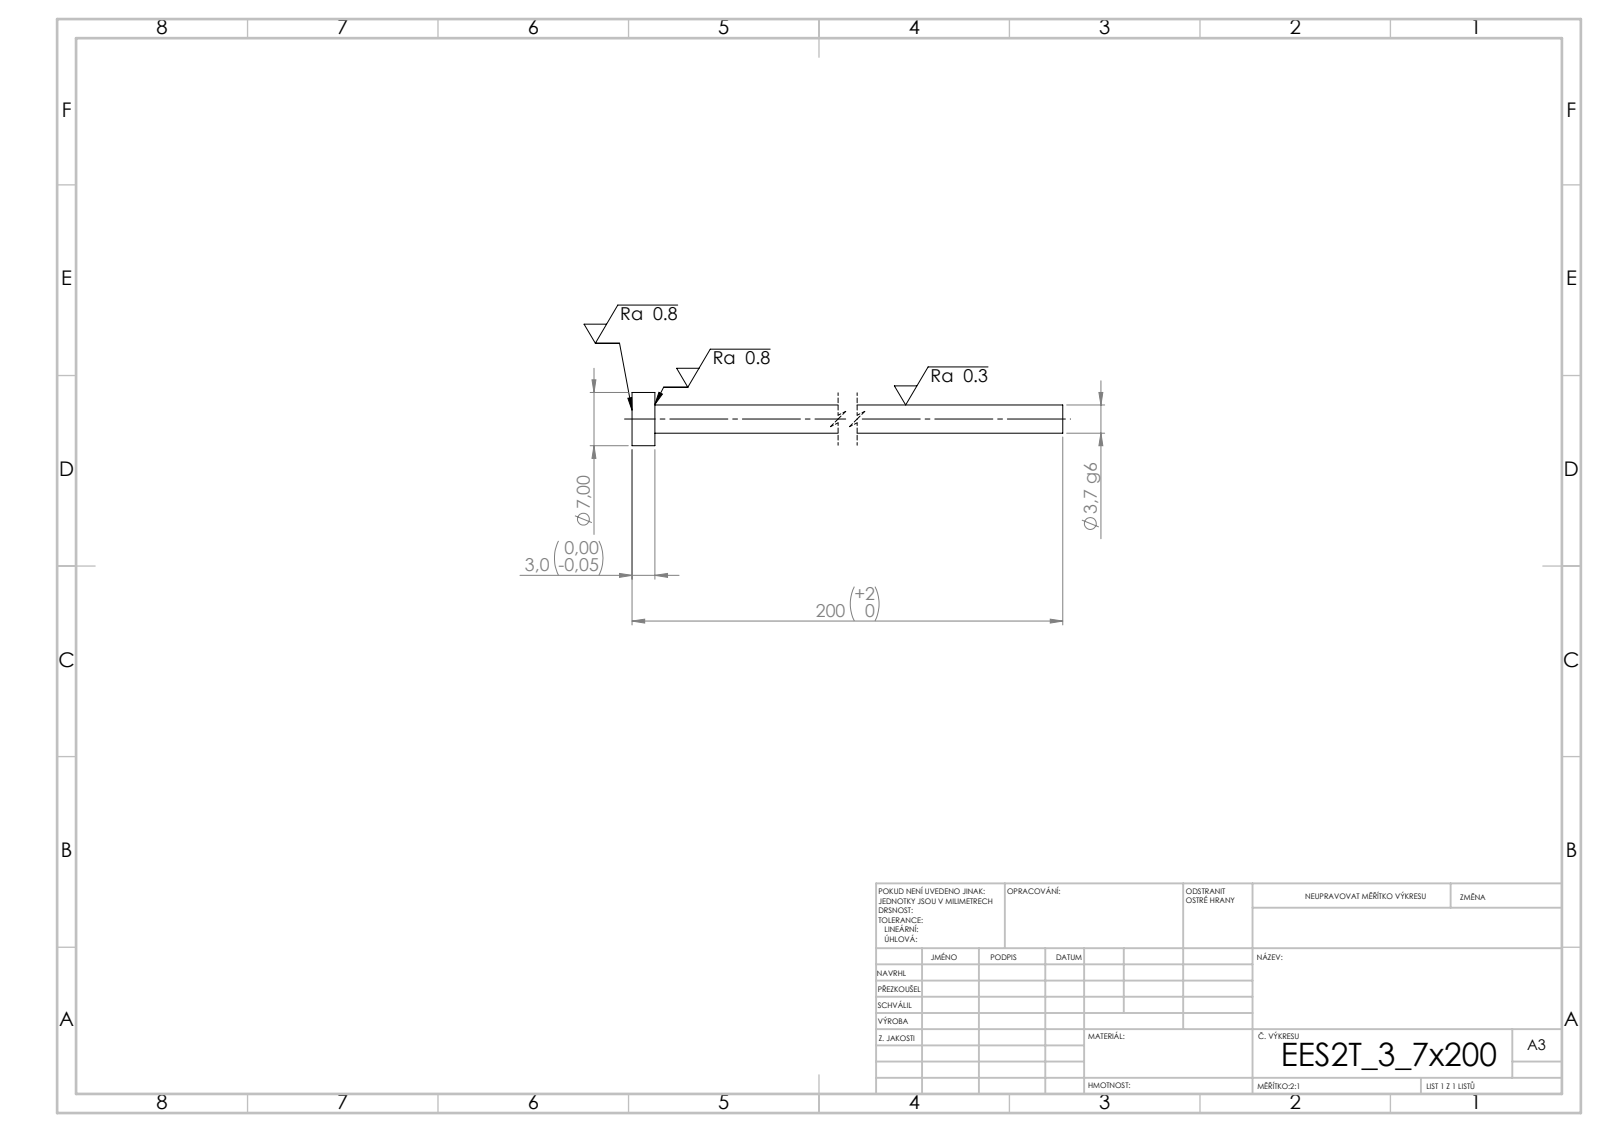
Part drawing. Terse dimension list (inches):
written by: SolidWorks 2019 (CONFIG_CONTROL_DESIGN)
unit: in
bodies: 1 solid, 7 faces (3 planar, 4 cylindrical, 0 other)
size: 7.874 × 0.276 × 0.276
volume: 0.136 in³; area: 3.771 in²
bosses: 1× ⌀0.276, 1× ⌀0.146
face distances: 0.118, 7.874, 7.756
